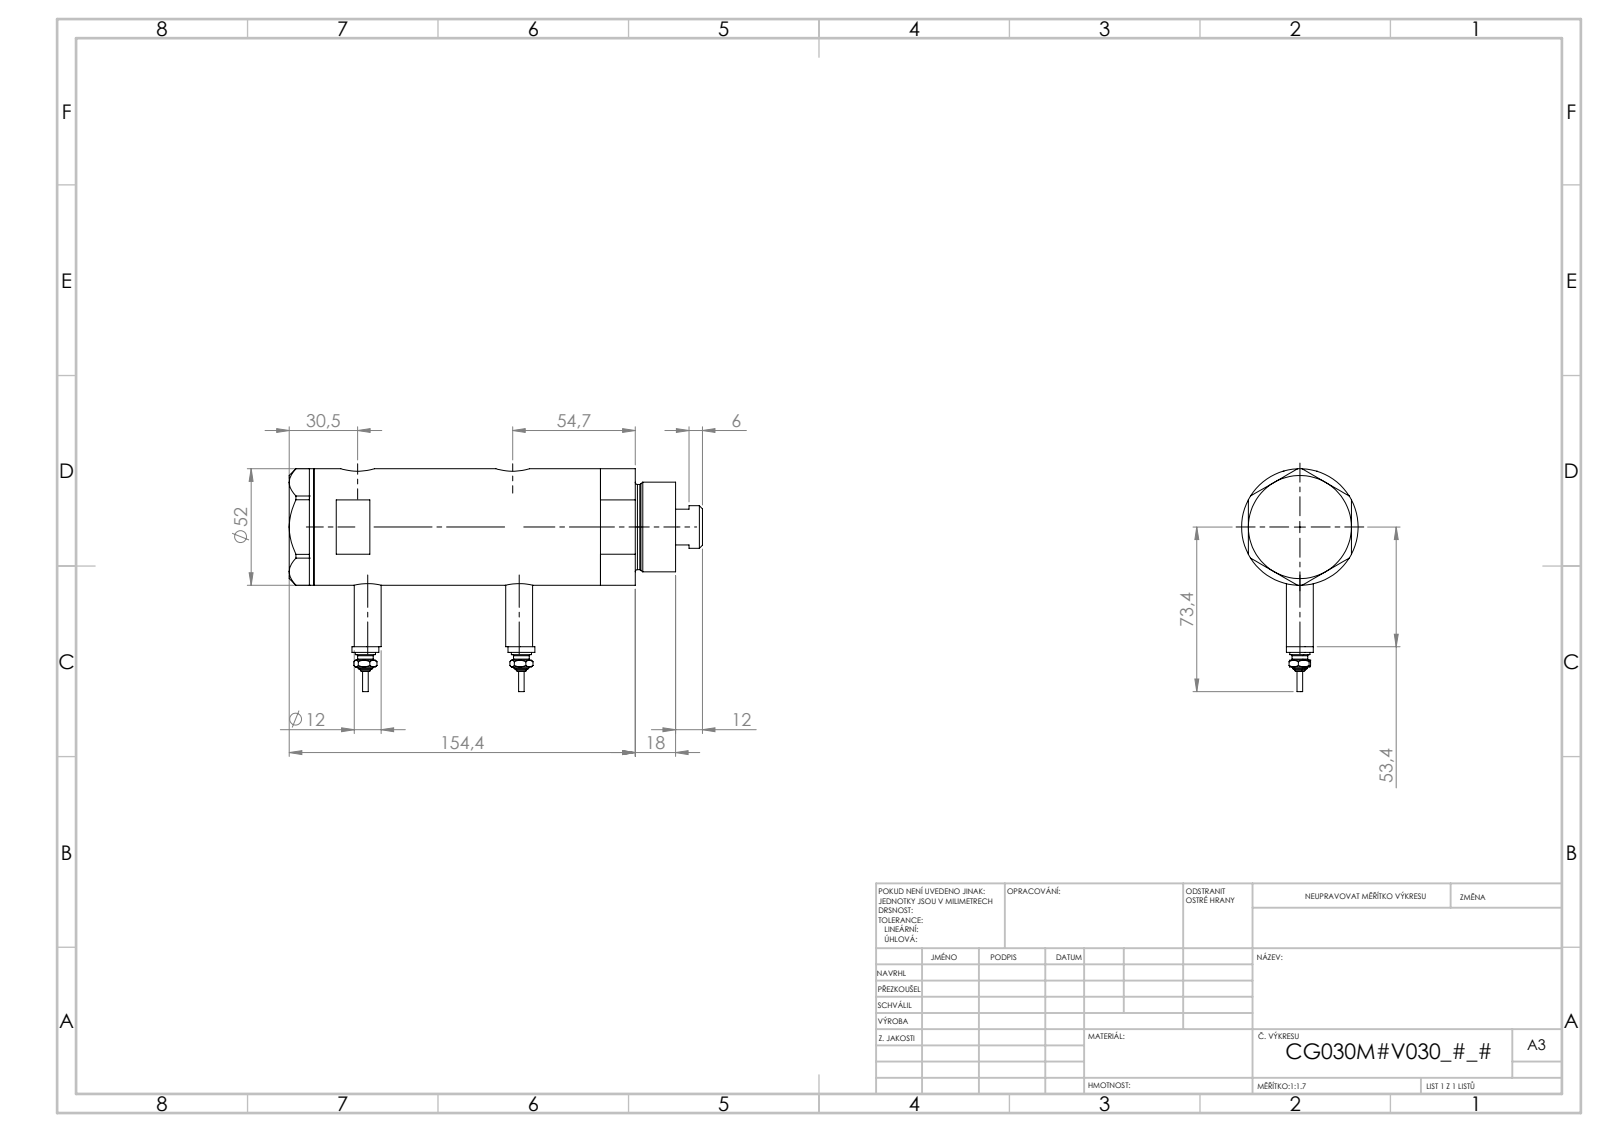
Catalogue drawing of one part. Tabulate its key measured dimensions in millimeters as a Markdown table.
| quantity | value |
| --- | --- |
| part name | V270CG_MIDDLE; V270CG_VC; V270CG_FRONT; V270CG_SWITCH (+1 more) |
| STEP written by | SolidWorks 2019 (CONFIG_CONTROL_DESIGN) |
| units | millimeters |
| bodies | 6 solids, 246 faces (95 planar, 77 cylindrical, 74 other) |
| overall size | 179.02 × 84.3 × 52 |
| volume | 322 306 mm³ |
| surface area | 76 649 mm² |
| round holes (diameter × count) | 5 × 2, 9.73 × 2, 12.5 × 2, 15 × 2, 6.5 × 1, 20 × 1, 21.5 × 1, 30 × 1, 33 × 1, 44 × 1 |
| round bosses / shafts (diameter × count) | 12 × 3, 9 × 2, 7 × 2, 4.34 × 2, 2.4 × 2, 52 × 1, 40 × 1, 38 × 1 |
| main face-to-face distances | 23.81, 10.99, 34.8, 46, 94.55, 83.56, 59.75, 130.95, 119.96, 96.15 |
| hole center spacings | 2.9, 4.5, 56.75, 59.65, 61.25, 64.15, 2.89, 2.91 |
